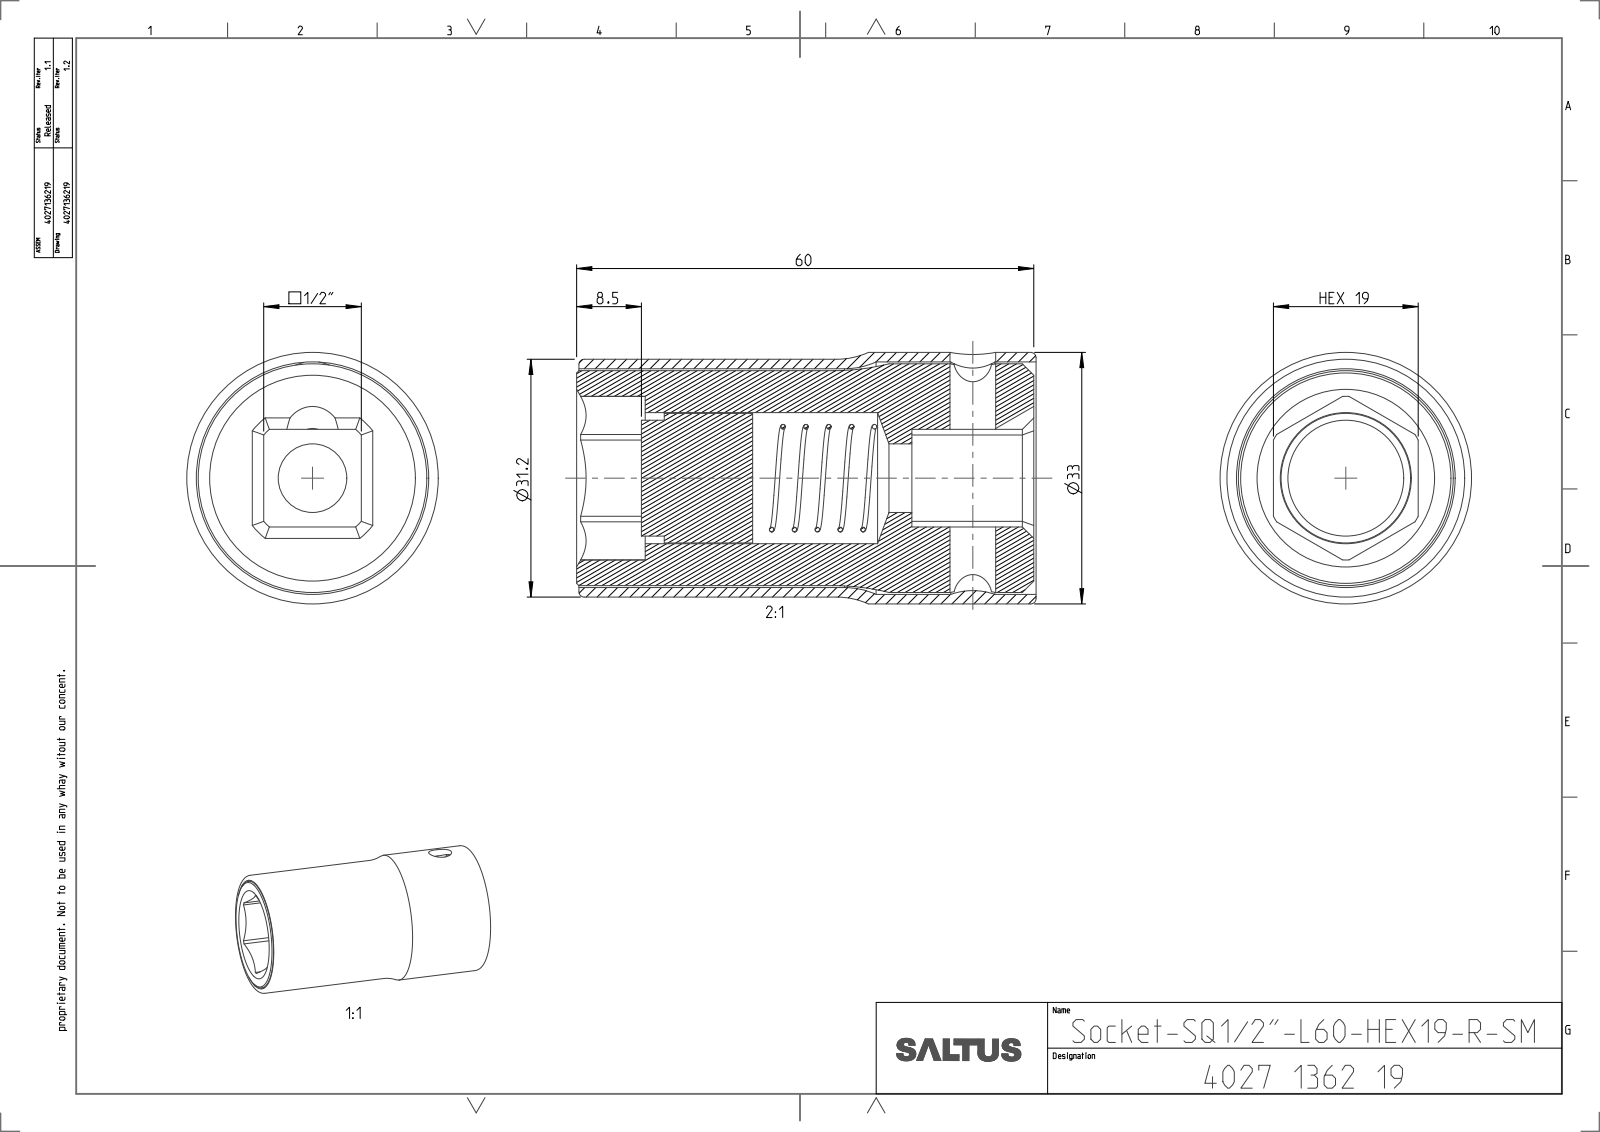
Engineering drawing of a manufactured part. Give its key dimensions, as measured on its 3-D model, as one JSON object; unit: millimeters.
{"part_name": "4027130719; 4027299385; 4027136219_ASM", "step_written_by": "CREO PARAMETRIC BY PTC INC, 2022414 (CONFIG_CONTROL_DESIGN)", "units": "millimeters", "bodies": {"solids": 4, "faces": 96, "planar": 26, "cylindrical": 41, "other": 29}, "overall_size": [60.3, 33, 33], "volume_mm3": 35686, "surface_area_mm2": 23206, "round_holes": [[6, 1], [9, 1], [17.2, 1], [28.7, 1], [30.5, 1]], "round_bosses_or_shafts": [[33, 1], [31.2, 1], [30, 1], [28.2, 1], [17, 1], [15.2, 1]], "partial_cylinders_radius": [[4, 1], [8.55, 1], [10.73, 1]], "face_to_face_distances": [12.82, 19, 36.9, 60, 51.5, 14.6, 23.1, 8.5, 3.09, 15.91]}
